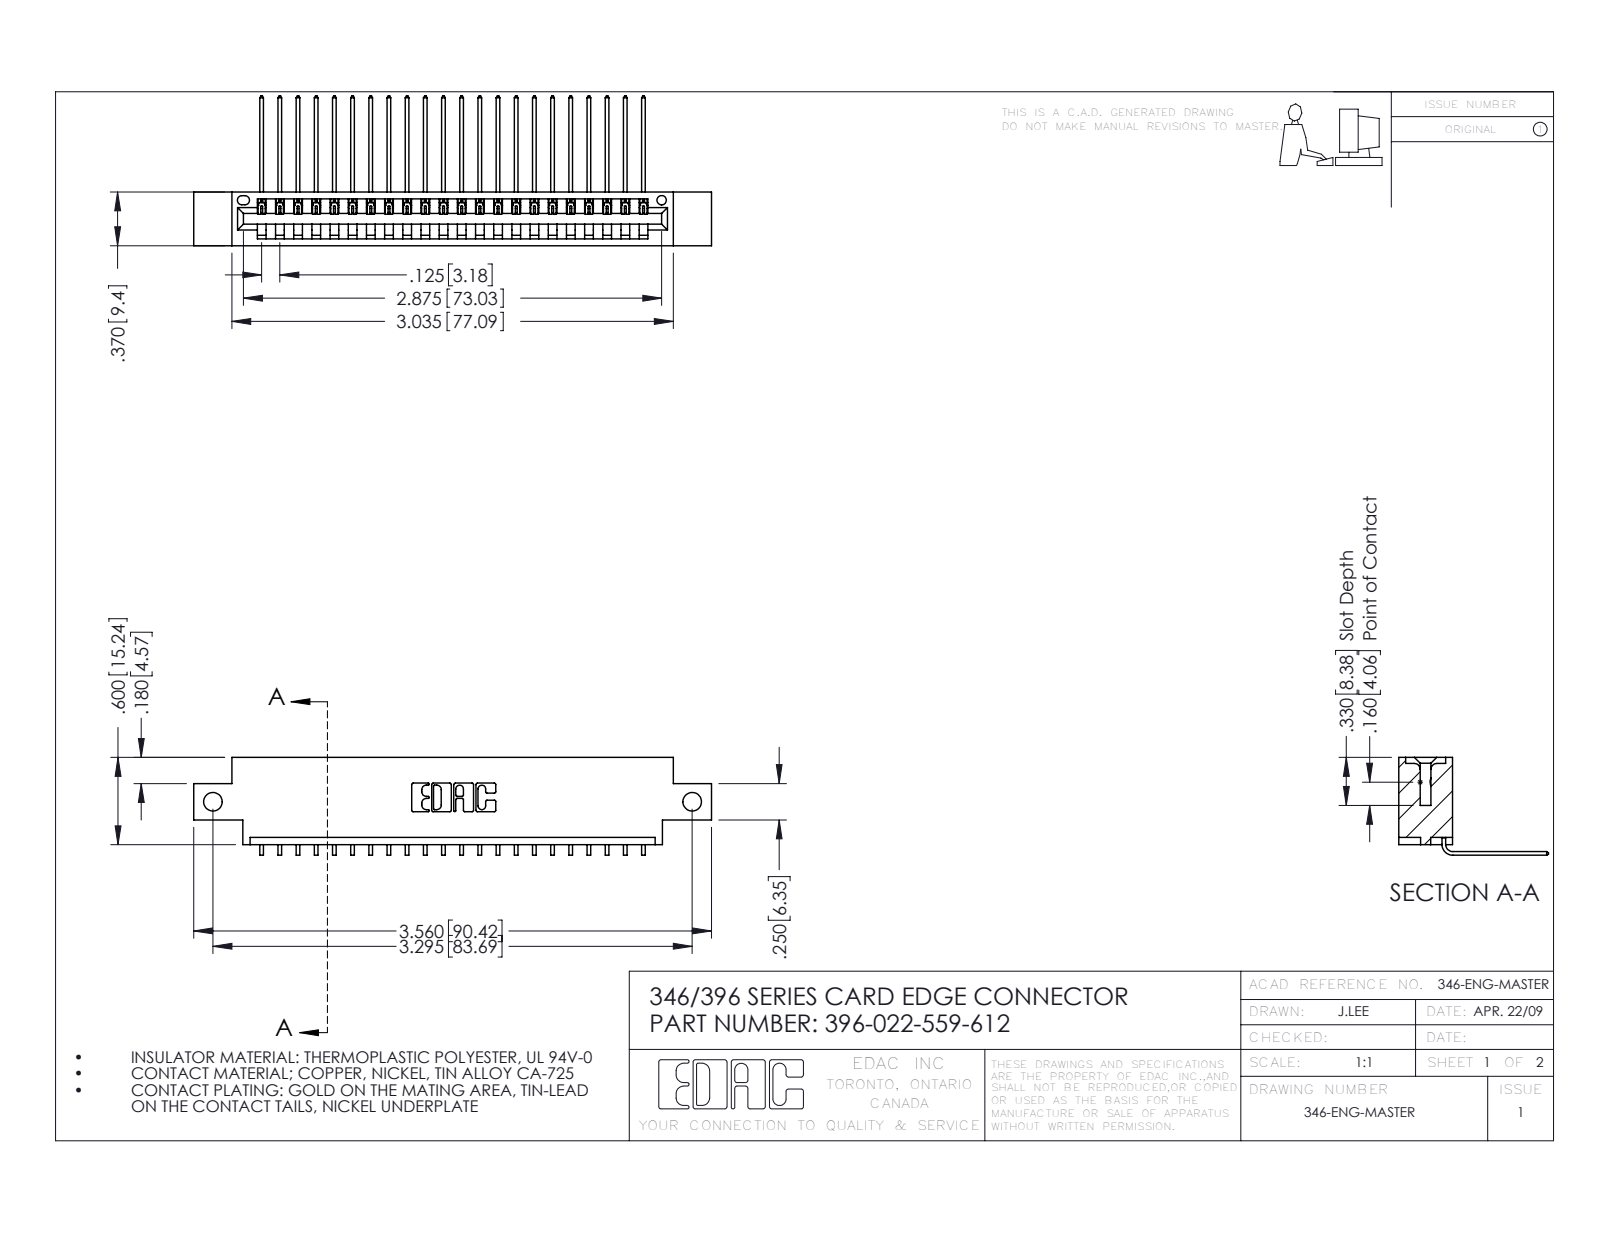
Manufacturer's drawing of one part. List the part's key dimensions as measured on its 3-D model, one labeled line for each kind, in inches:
Part name (STEP PRODUCT): 396-022-559-612; 346 Part_0.170 Offset - Side Mount; 345-292-001_558 559 Tail - 1
STEP written by: SolidWorks 2016 (CONFIG_CONTROL_DESIGN)
Units: inches
Bodies: 23 solids, 1446 faces (1004 planar, 442 cylindrical, 0 other)
Overall size (bounding box): 3.56 × 1.03 × 0.673
Volume: 0.509 in³ · Surface area: 16.54 in²
Round holes (diameter × count): ⌀0.128 ×2, ⌀0.064 ×1
Partial cylindrical surfaces — rounded edges, fillets, slot ends (radius × count): R0.006 ×44, R0.01 ×22, R0.007 ×6, R0.031 ×6, R0.026 ×3, R0.031 ×2, R0.04 ×2, R0.014 ×1
Main face-to-face distances: 0.048, 0.37, 0.322, 0.25, 0.025, 0.072, 0.148, 0.222, 0.1, 0.174
Hole centre spacings: 3.295
